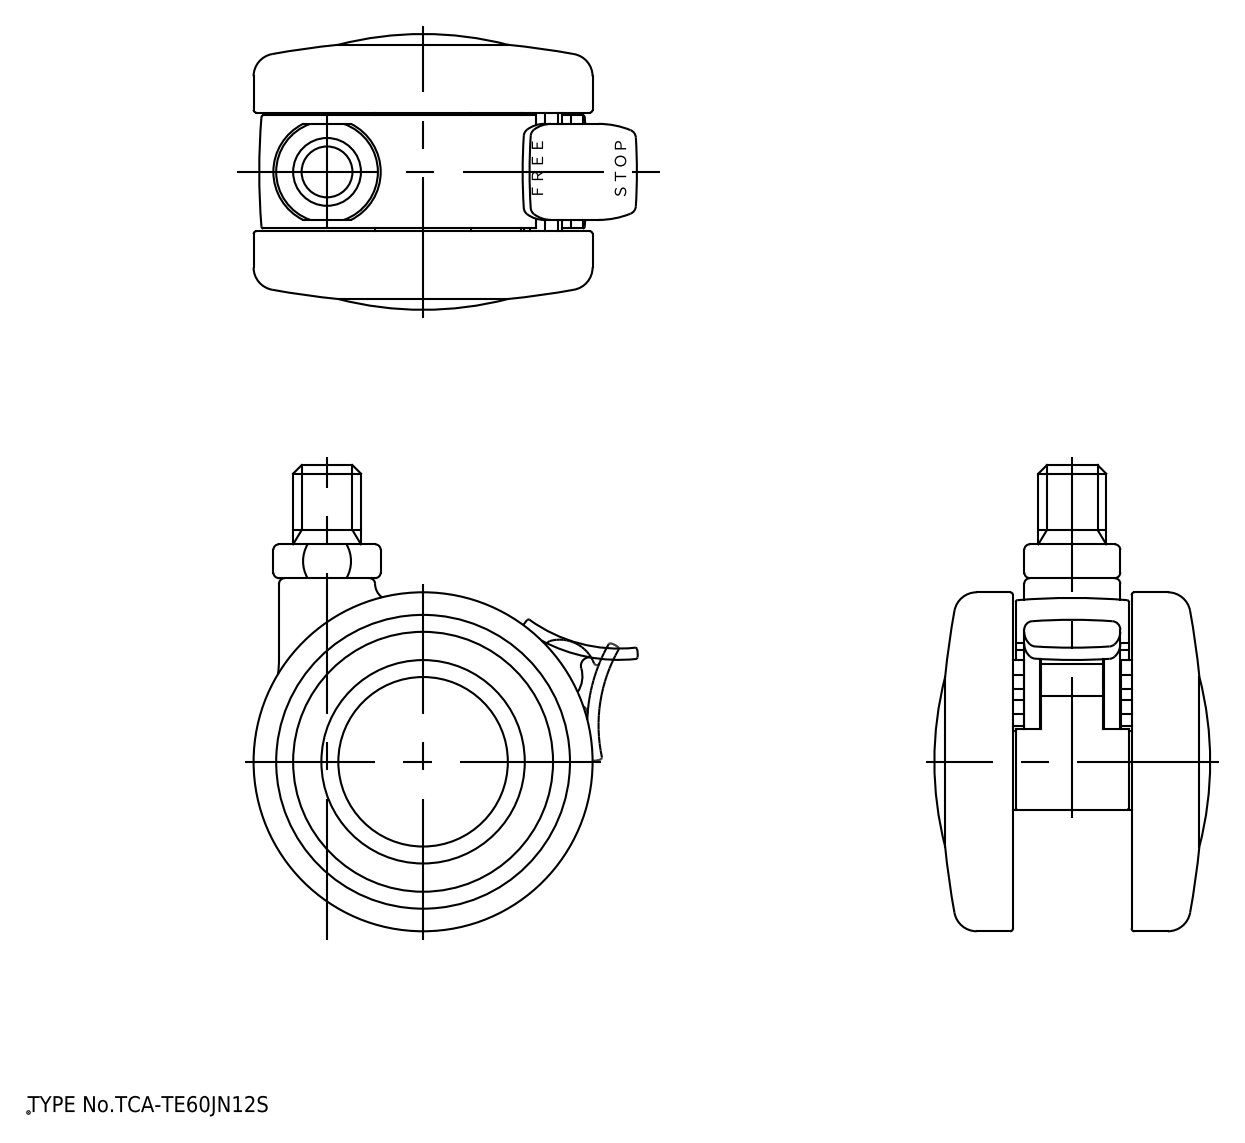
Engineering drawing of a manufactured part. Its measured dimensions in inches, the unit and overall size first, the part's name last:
Units: inches
Overall size (bounding box): 3.248 × 2.711 × 1.935
Round holes (diameter × count): ⌀0.138 ×1, ⌀0.315 ×1, ⌀0.366 ×1, ⌀0.421 ×1, ⌀0.787 ×1, ⌀1.189 ×1, ⌀1.772 ×1
Round bosses / shafts (diameter × count): ⌀2.362 ×1, ⌀1.417 ×1, ⌀1.177 ×1, ⌀0.709 ×1, ⌀0.669 ×1, ⌀0.472 ×1, ⌀0.413 ×1, ⌀0.256 ×1
Partial cylindrical surfaces — rounded edges, fillets, slot ends (radius × count): R0.012 ×6, R0.039 ×5, R0.059 ×5, R0.079 ×5, R0.591 ×2, R1.043 ×2, R1.142 ×2, R3.926 ×2
Main face-to-face distances: 0.197, 0.433, 0.079, 1.024, 0.276, 1.201, 0.748, 0.945, 0.827, 1.122
Hole centre spacings: 1.083
Volume: 5.233 in³ · Surface area: 52.52 in²
Bodies: 5 solids, 260 faces (67 planar, 114 cylindrical, 79 other)
Part name (STEP PRODUCT): TCA-TE60J_Wheel; TCA-TE60JN12_Shaft; TCA-TE60JS_Body; TCA-TE60JS_Stopper
STEP written by: spGate 18.9.1 (****-****-****-****) (AUTOMOTIVE_DESIGN)
